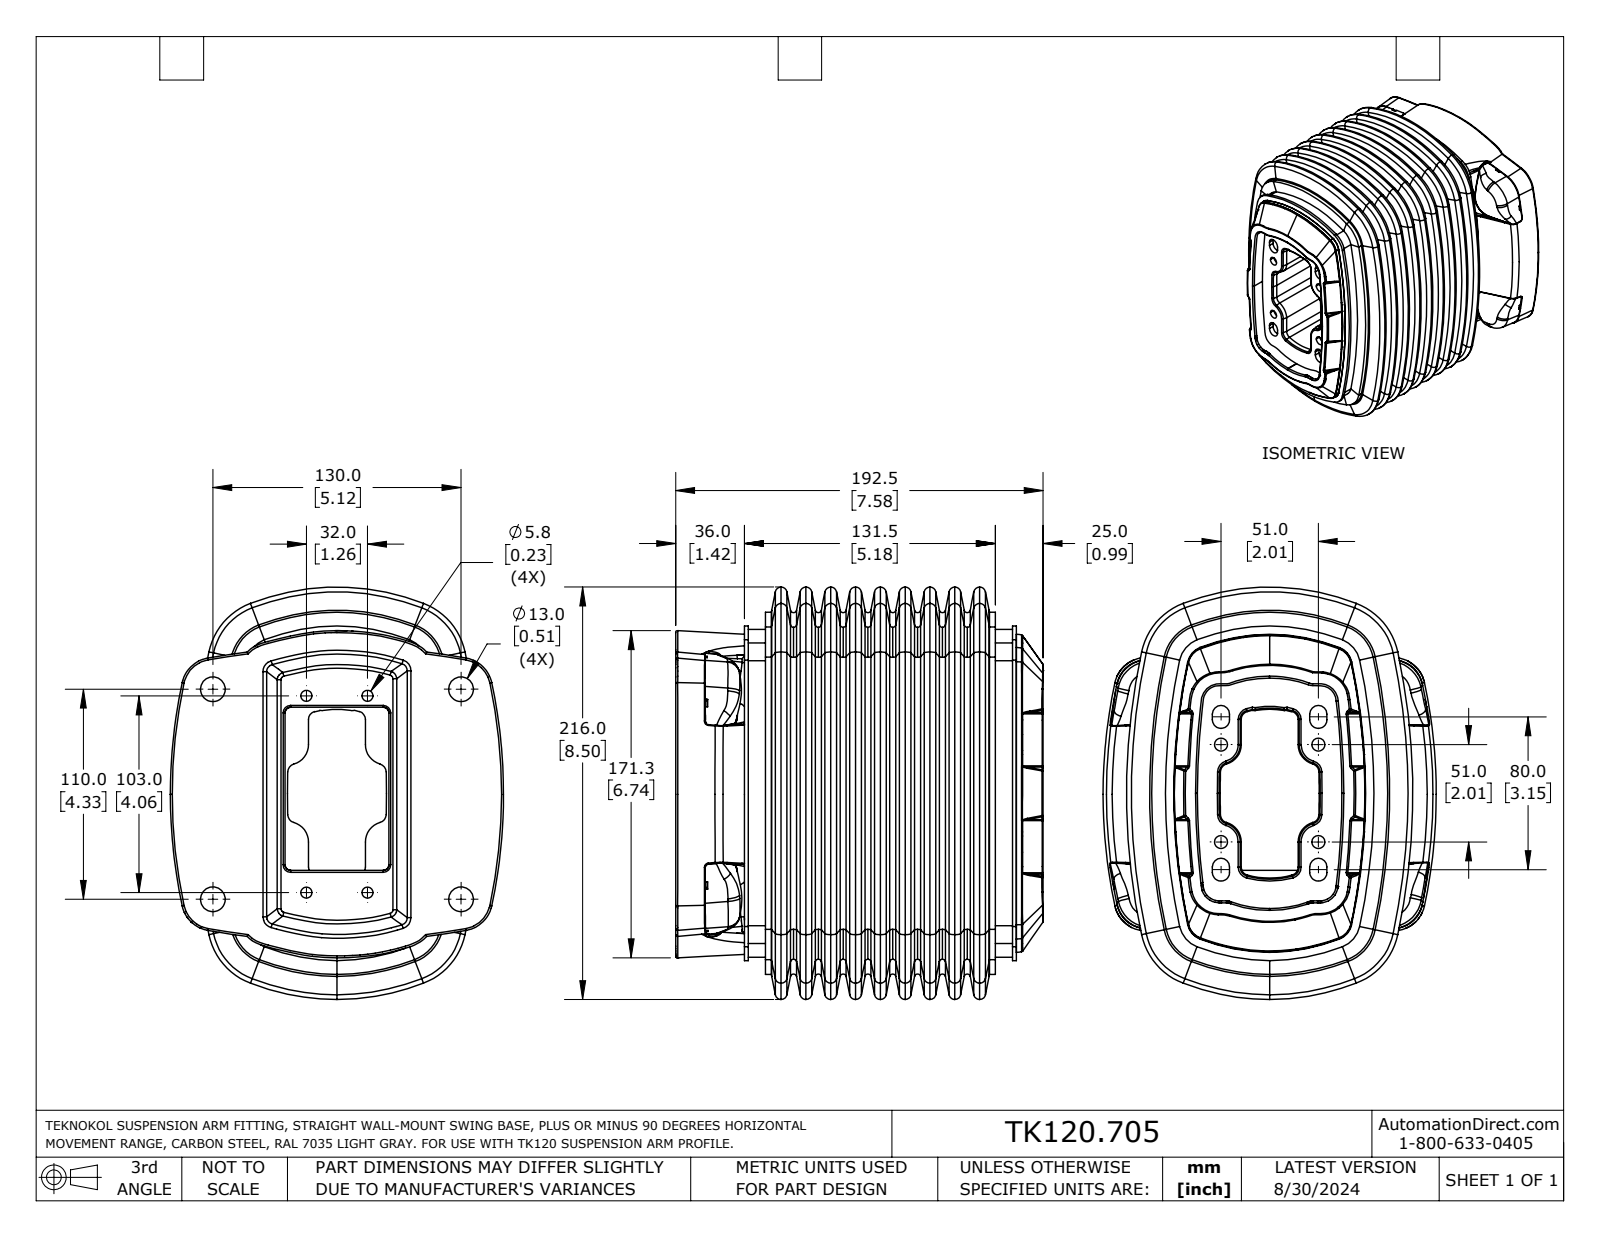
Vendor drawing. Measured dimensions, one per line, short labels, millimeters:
written by: SolidWorks 2023 (AUTOMOTIVE_DESIGN)
unit: mm
bodies: 1 solid, 1094 faces (140 planar, 70 cylindrical, 884 other)
size: 216 × 192.1 × 174.5
volume: 3 486 000 mm³; area: 321 200 mm²
holes: 4× ⌀6.8, 4× ⌀13
rounds: 8× R4.5, 4× R4.3, 4× R4.4, 4× R10.6, 4× R13.6, 4× R17.6, 2× R1, 2× R3.1
face distances: 35.2, 132.2, 167.5, 120.5, 11.8, 47, 152, 31.5, 19.7, 15.5
hole spacings: 49.3, 51, 89.7, 95.2, 121.1, 72.1, 110, 130
